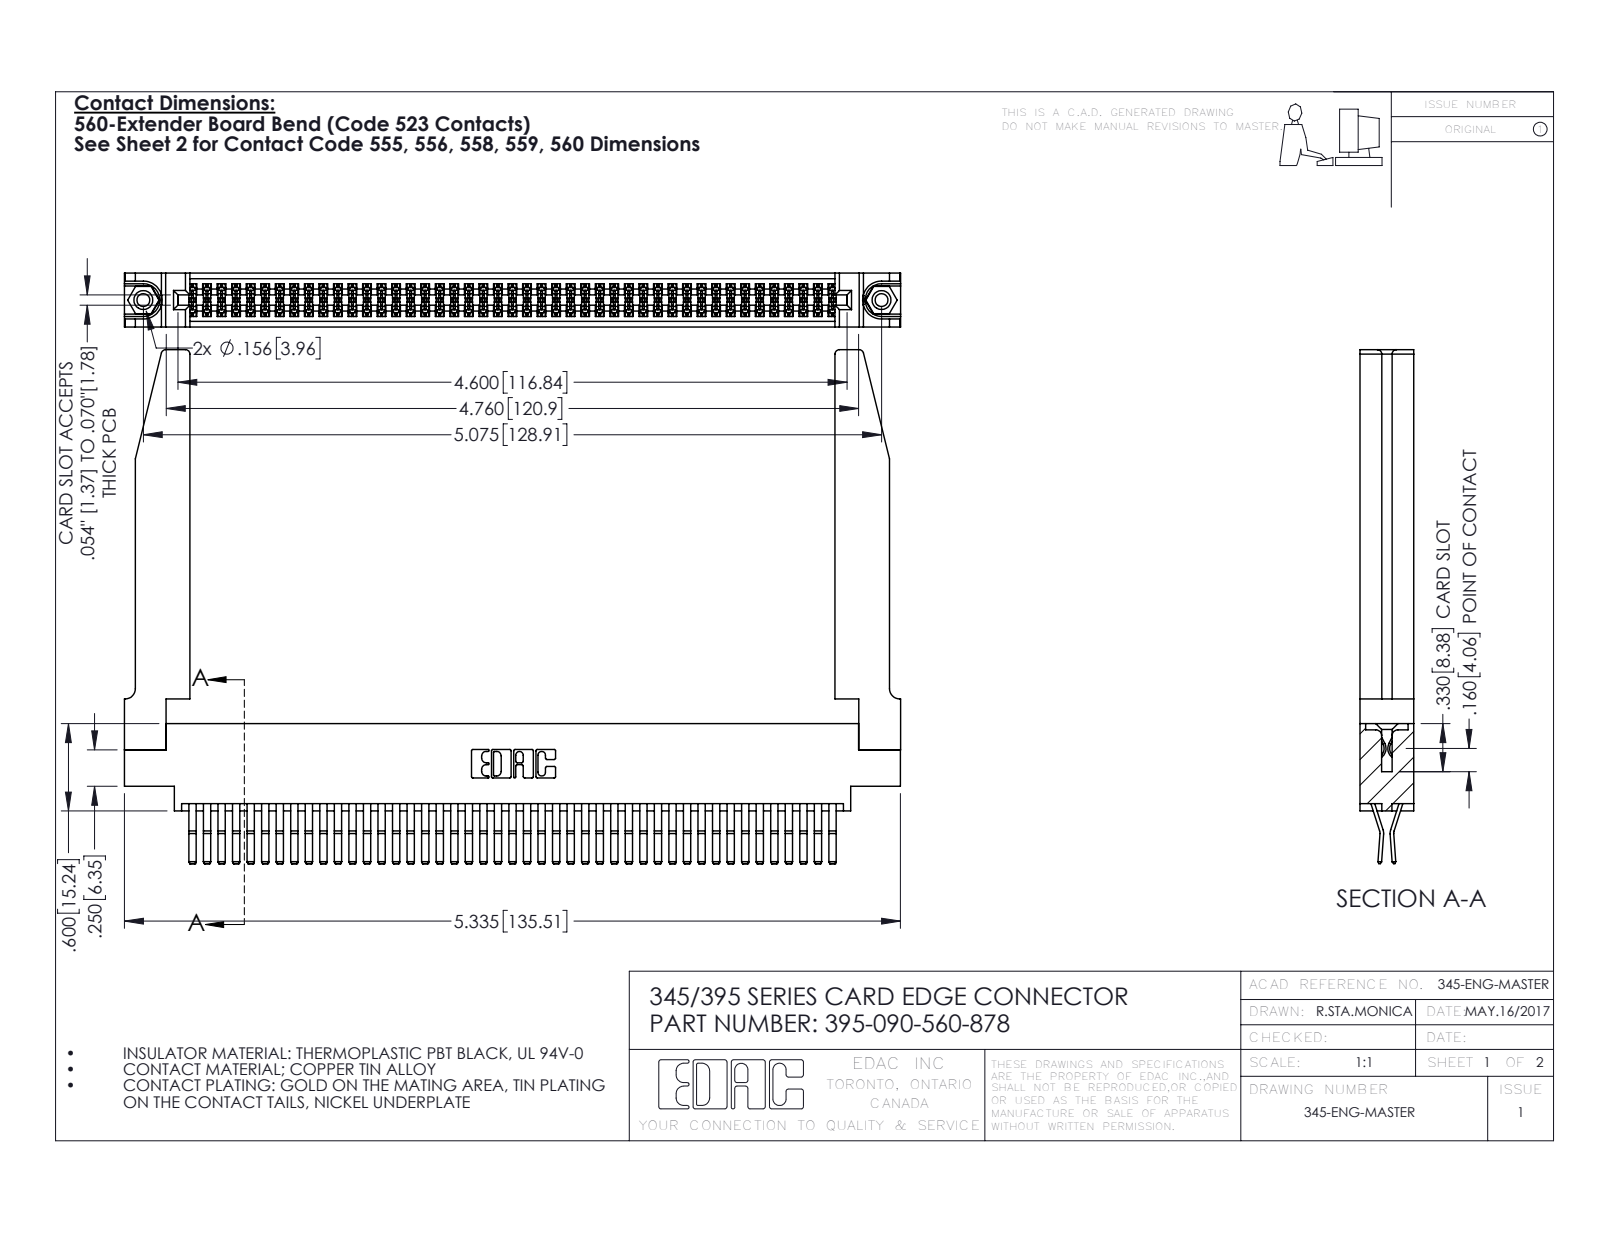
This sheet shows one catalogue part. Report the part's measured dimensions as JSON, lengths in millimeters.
{"part_name": "395-090-560-878; 345-250-001_345-250-001-102; 345-220-078_345-220-078; 345 Part_0.170 Offset - 0.156 Dia-TH (+1 more)", "step_written_by": "SolidWorks 2016 (CONFIG_CONTROL_DESIGN)", "units": "millimeters", "bodies": {"solids": 95, "faces": 5044, "planar": 3196, "cylindrical": 1796, "other": 52}, "overall_size": [135.5, 89.7, 9.4], "volume_mm3": 21430, "surface_area_mm2": 28760, "round_holes": [[2.3, 2], [3.2, 2], [4, 2], [1.6, 1]], "round_bosses_or_shafts": [[3.9, 2]], "partial_cylinders_radius": [[0.2, 135], [0.3, 22], [0.8, 8], [0.2, 6], [0.8, 6], [0.7, 3], [0.3, 2], [0.4, 2]], "face_to_face_distances": [9.4, 1.8, 7.6, 0.6, 2.5, 6.9, 5.1, 5.7, 4.4, 3.8], "hole_center_spacings": [6.9, 122.9, 128.9]}
